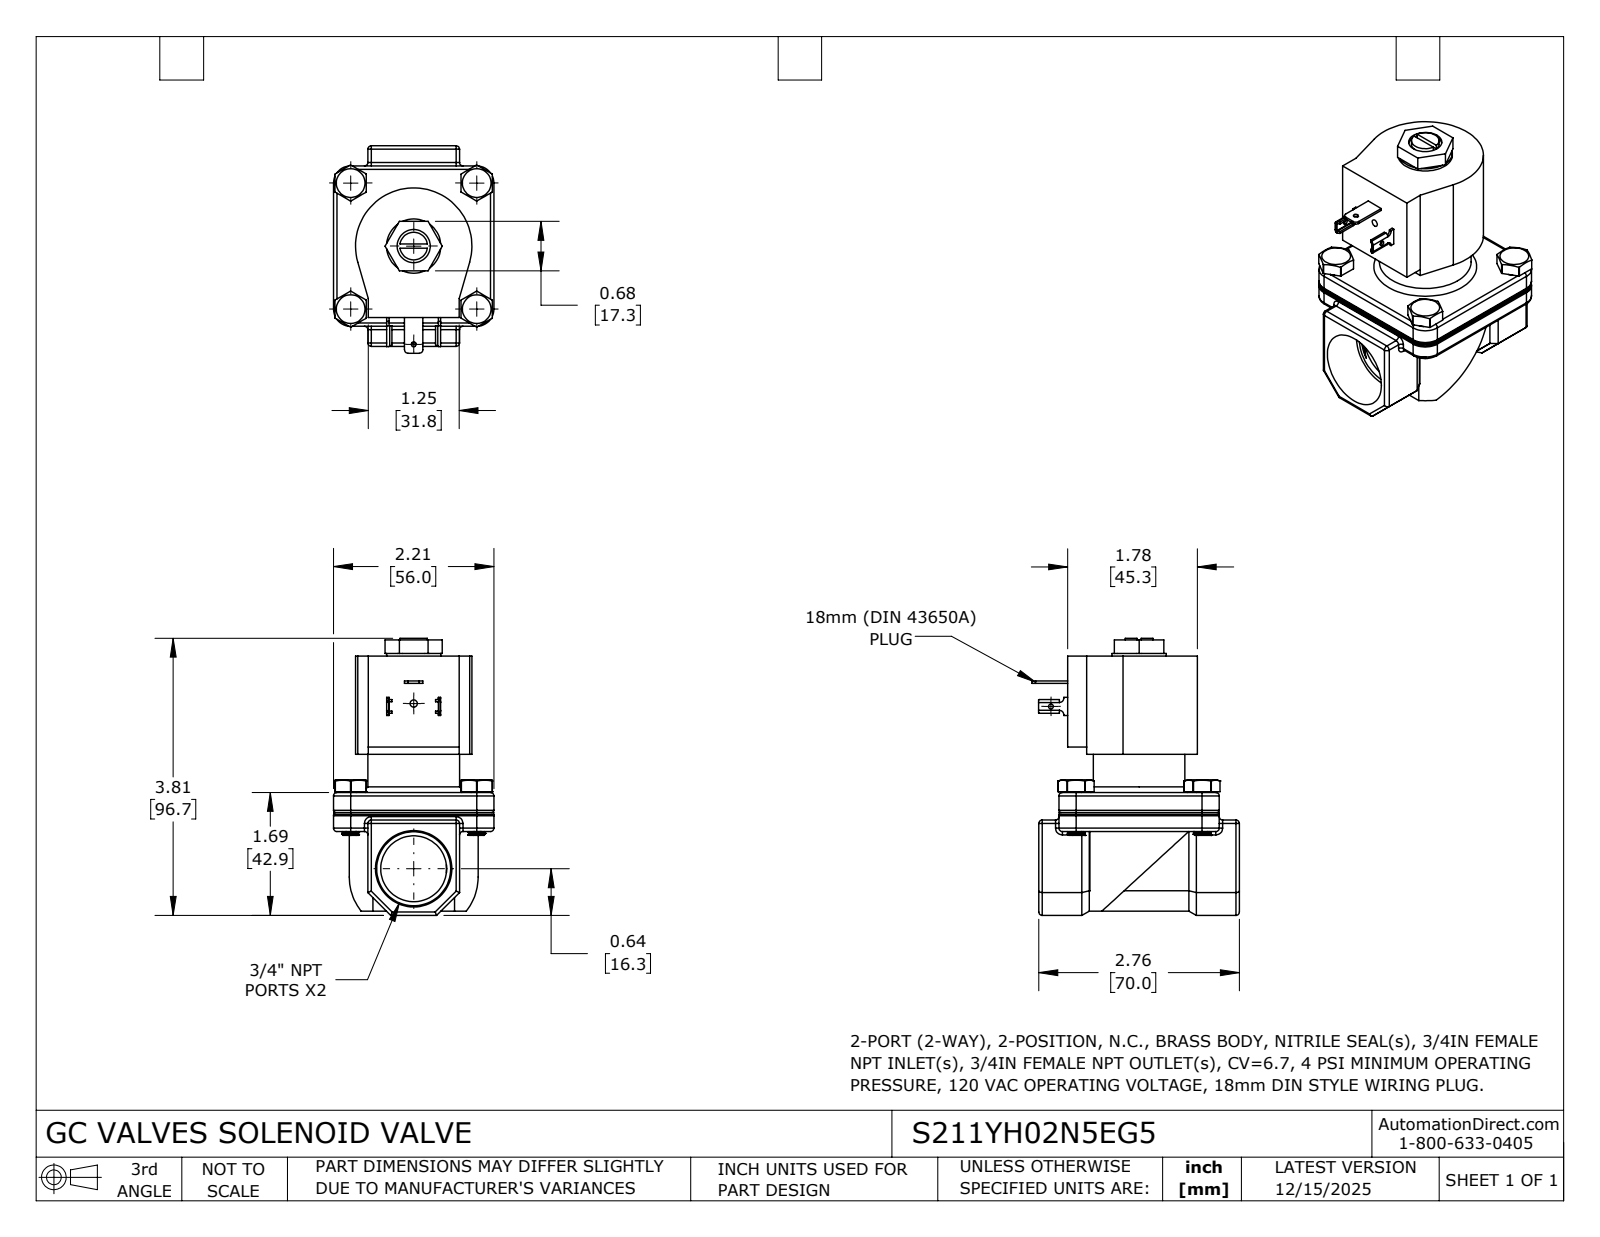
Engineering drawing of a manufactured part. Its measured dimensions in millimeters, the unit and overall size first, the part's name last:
Units: millimetres
Overall size (bounding box): 96.7 × 72.4 × 56
Round holes (diameter × count): ⌀1.7 ×1, ⌀1.7 ×1, ⌀2.5 ×1, ⌀11.6 ×1, ⌀23 ×1
Round bosses / shafts (diameter × count): ⌀10.3 ×4, ⌀6.1 ×4, ⌀32 ×1, ⌀18.9 ×1, ⌀9.7 ×1
Partial cylindrical surfaces — rounded edges, fillets, slot ends (radius × count): R1.2 ×34, R0.2 ×4, R0.8 ×4, R1 ×4, R5.9 ×4, R6 ×4, R1.3 ×2, R1.5 ×2
Main face-to-face distances: 1.5, 47.6, 12, 44, 13.6, 61.2, 56, 27.8, 41.4, 89
Hole centre spacings: 34.3, 57.7
Volume: 154 700 mm³ · Surface area: 28 060 mm²
Bodies: 1 solid, 402 faces (195 planar, 131 cylindrical, 76 other)
Part name (STEP PRODUCT): S211YH02N5EG5
STEP written by: SolidWorks 2024 (CONFIG_CONTROL_DESIGN)
